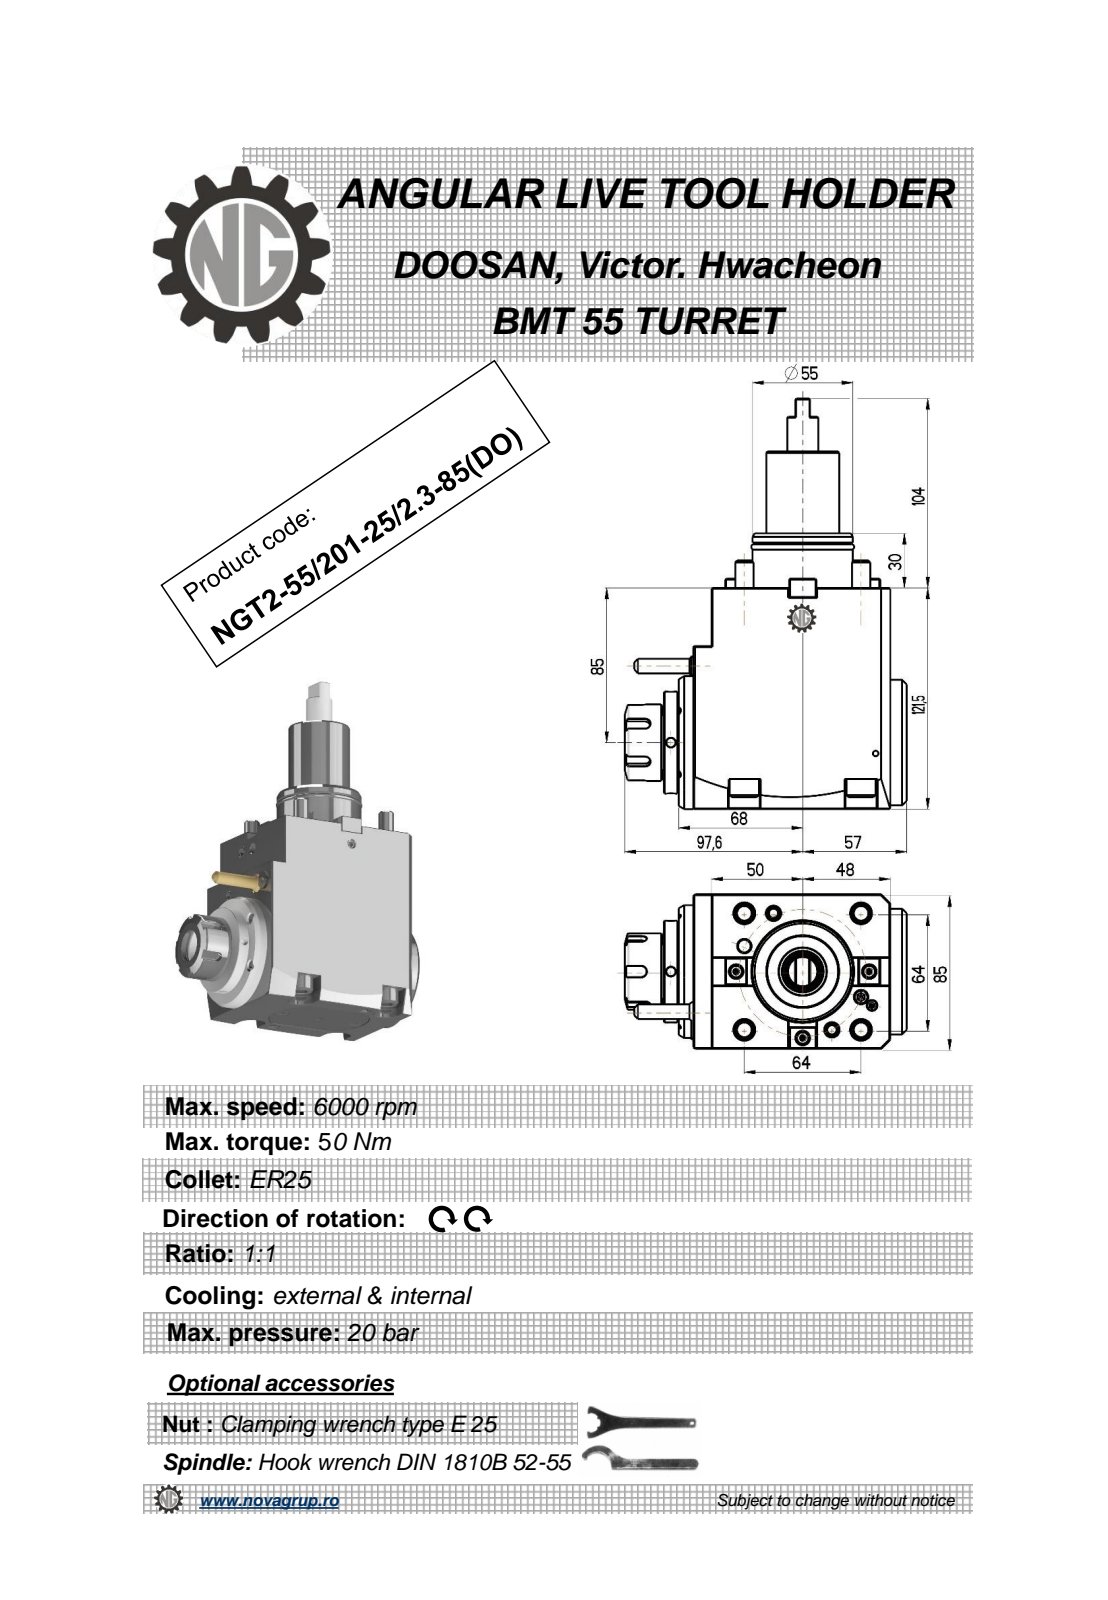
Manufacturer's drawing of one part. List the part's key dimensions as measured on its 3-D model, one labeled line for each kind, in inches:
Part name (STEP PRODUCT): NGT2_55_201_25_1_3_85_DO
STEP written by: PRO/ENGINEER BY PARAMETRIC TECHNOLOGY CORPORATION, 2010280 (CONFIG_CONTROL_DESIGN)
Units: inches
Bodies: 2 solids, 482 faces (228 planar, 109 cylindrical, 145 other)
Overall size (bounding box): 8.878 × 6.138 × 3.346
Volume: 80.12 in³ · Surface area: 175.8 in²
Round holes (diameter × count): ⌀0.197 ×3, ⌀0.268 ×2, ⌀0.118 ×1, ⌀0.472 ×1
Round bosses / shafts (diameter × count): ⌀0.63 ×4, ⌀0.394 ×4, ⌀2.874 ×1, ⌀2.677 ×1, ⌀2.205 ×1, ⌀2.165 ×1, ⌀1.969 ×1, ⌀1.709 ×1
Partial cylindrical surfaces — rounded edges, fillets, slot ends (radius × count): R0.013 ×20, R0.009 ×6, R0.118 ×5, R0.335 ×4, R0.031 ×2, R18.898 ×2
Main face-to-face distances: 3.346, 4.783, 0.315, 0.394, 0.406, 4.252, 4.657, 3.858, 4.264, 0.709
Hole centre spacings: 1.678, 2.75, 4.141
